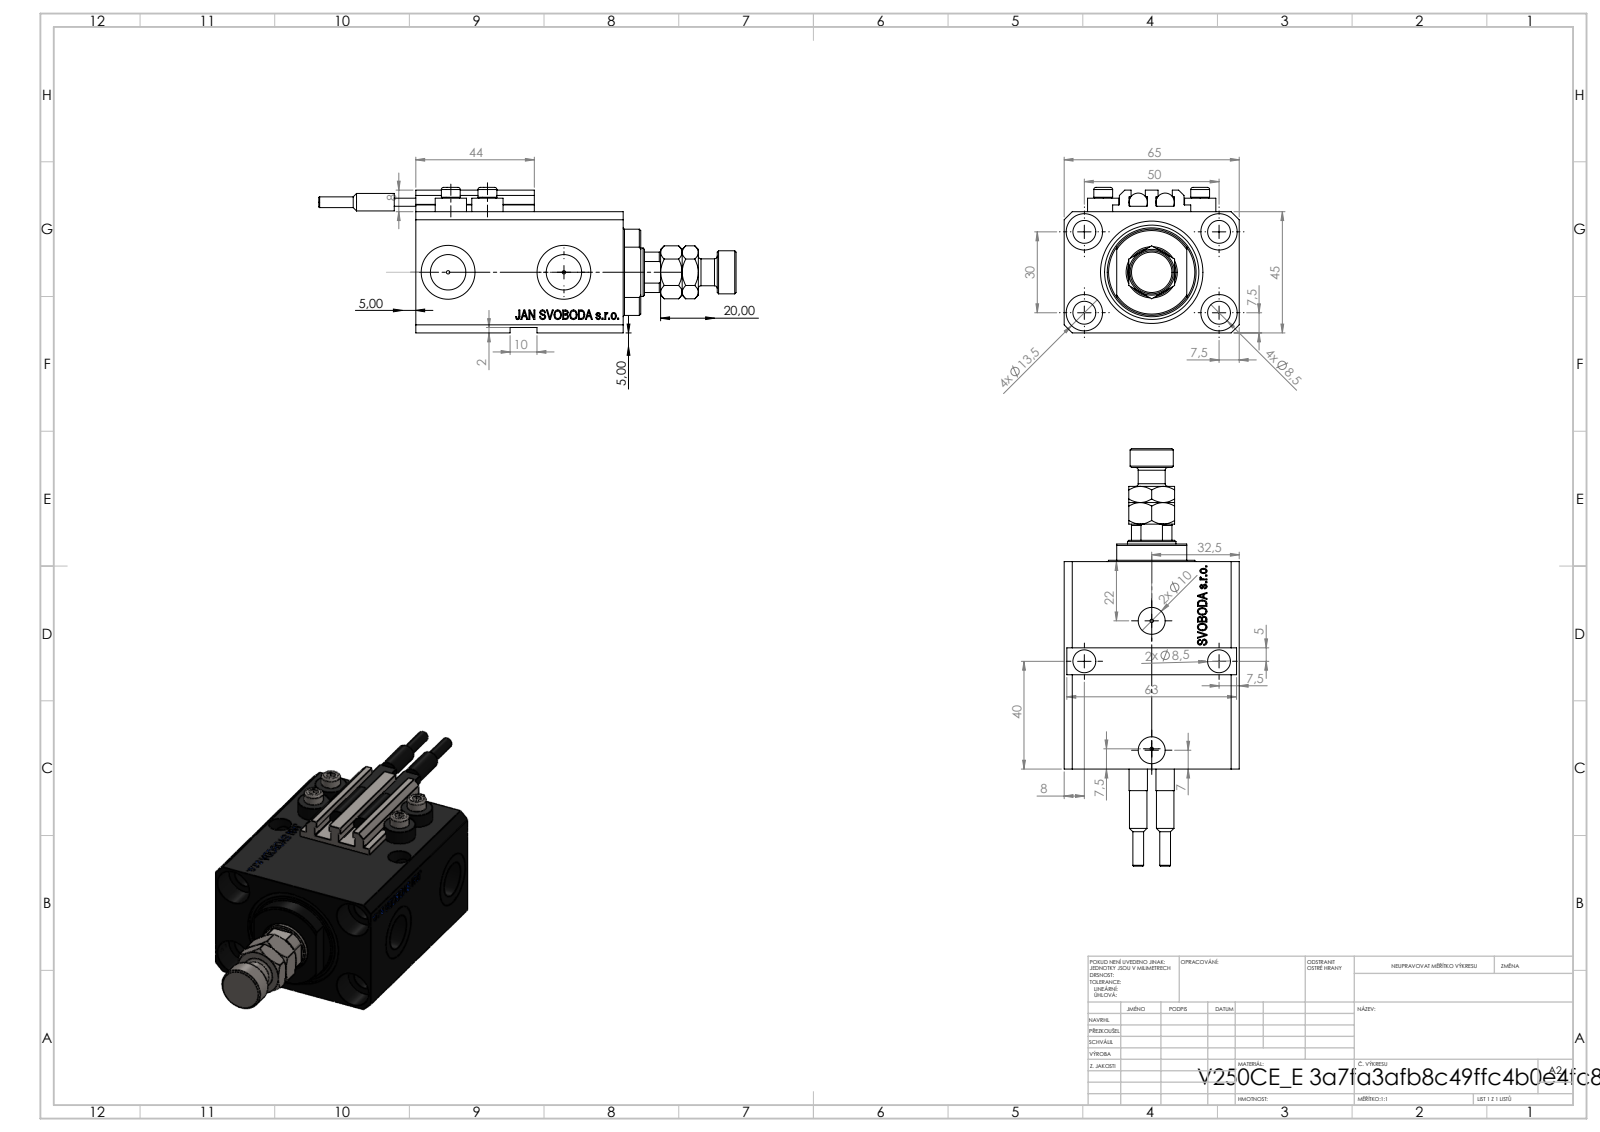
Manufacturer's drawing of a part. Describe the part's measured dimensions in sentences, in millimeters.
The part is named "MFA; ALLEN BOLT V250CE; V250CE_E_Body; SWITCH_V250CE (+2 more)". Its 3-D file was written by "SolidWorks 2019 (CONFIG_CONTROL_DESIGN)". It is 11 solids with 1187 faces: 563 planar, 154 cylindrical and 470 other. Overall it measures 155 by 65 by 54 millimeters. Its volume is 205 157 cubic millimeters and its surface area 65 137 square millimeters. Round holes: 7 of diameter 8.5, 4 of diameter 1.25, 4 of diameter 4, 4 of diameter 13.5, 2 of diameter 10, 2 of diameter 13.16, 2 of diameter 20, 1 of diameter 18, 1 of diameter 25, 1 of diameter 38. Round bosses or shafts: 4 of diameter 11.6, 4 of diameter 7, 2 of diameter 6.8, 2 of diameter 6.5, 2 of diameter 4, 1 of diameter 16, 1 of diameter 10. Partial cylindrical surfaces (rounded edges, fillets, slot ends): 10 of radius 0.2, 1 of radius 8.5, 1 of radius 16. The main face-to-face distances are 45, 65, 14, 63, 2, 77, 3, 6.9, 47, 5. The hole center spacings are 29.15, 50, 13.6, 15.12, 18.81, 18.97, 26.22, 26.61.
